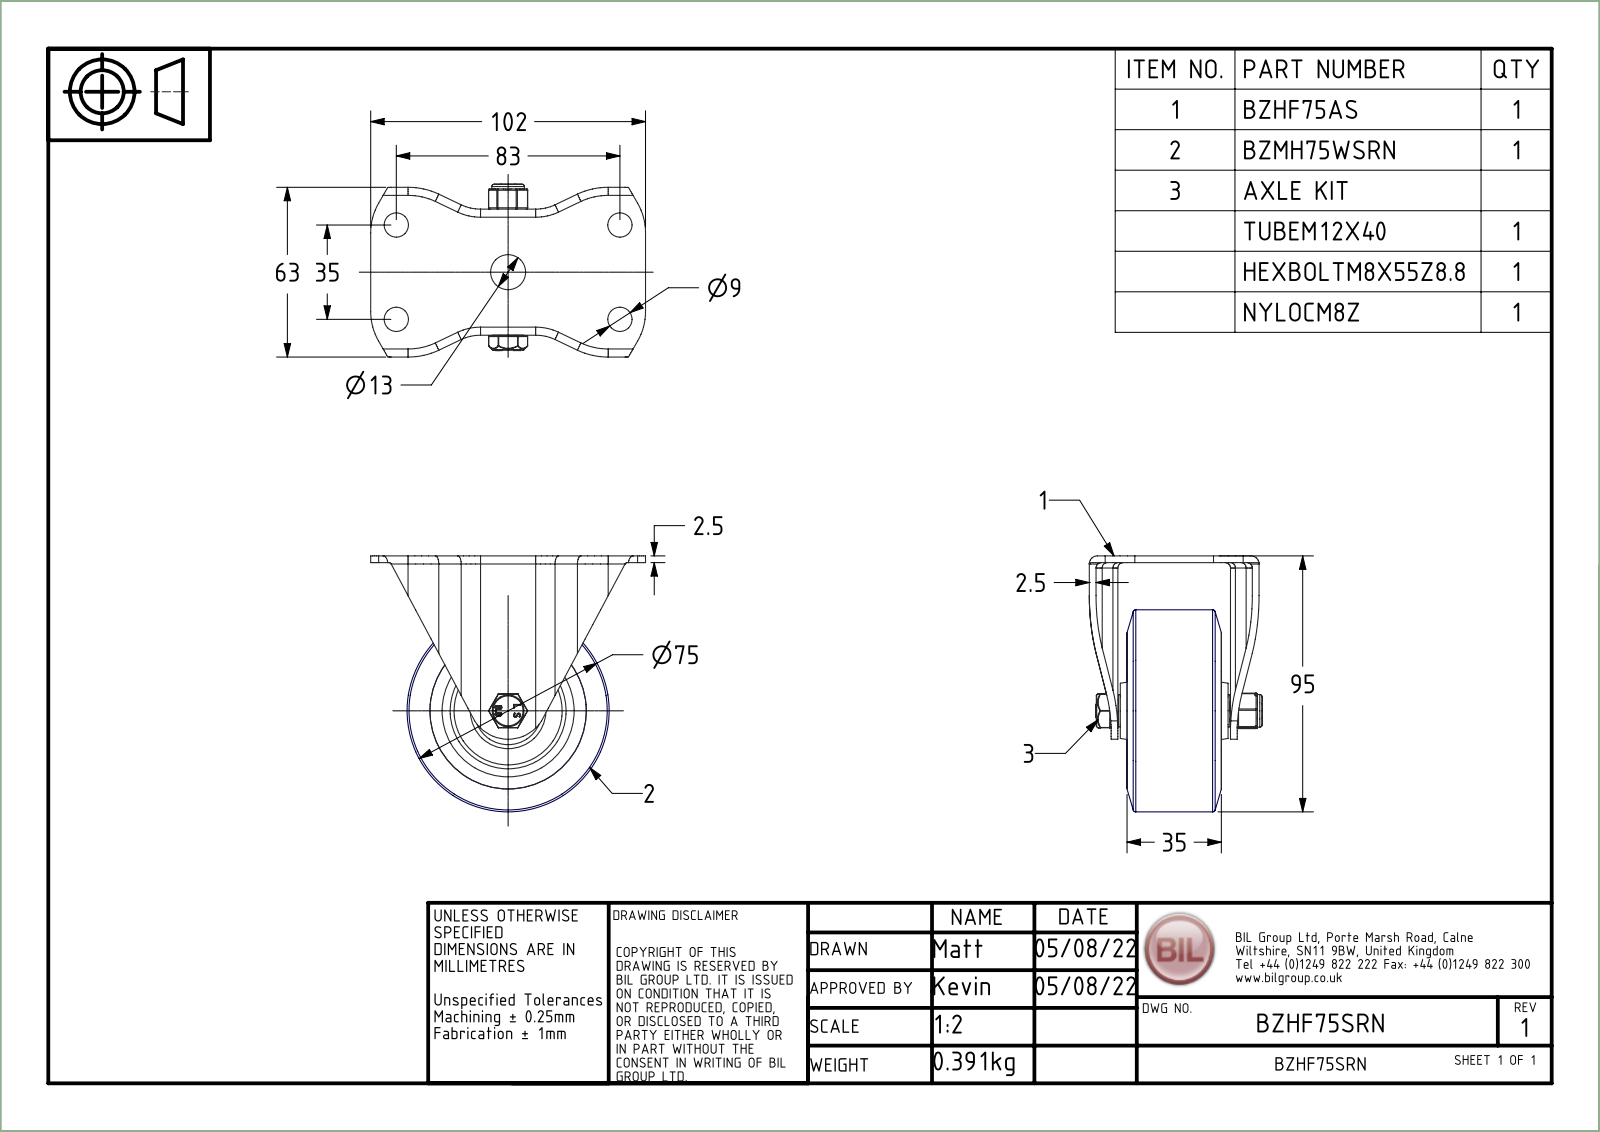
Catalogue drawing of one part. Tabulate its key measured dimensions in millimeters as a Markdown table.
| quantity | value |
| --- | --- |
| part name | BZHF75AS; ZINC PLATED, PRESSED STEEL BRACKET; BZHF75SRN; BZMH75WSRN (+8 more) |
| STEP written by | Spatial InterOp 3D (AUTOMOTIVE_DESIGN) |
| units | millimeters |
| bodies | 7 solids, 430 faces (97 planar, 213 cylindrical, 120 other) |
| overall size | 102 × 95 × 64.15 |
| volume | 149 419 mm³ |
| surface area | 66 315 mm² |
| round holes (diameter × count) | 9 × 4, 0.66 × 2, 8 × 1, 8.2 × 1, 8.4 × 1, 8.6 × 1, 12.2 × 1, 13 × 1, 58 × 1 |
| round bosses / shafts (diameter × count) | 75 × 1, 12.1 × 1, 11.9 × 1, 11.5 × 1, 6.75 × 1 |
| partial cylindrical surfaces (radius × count) | 0.5 × 18, 0.25 × 12, 2 × 8, 3 × 8, 0.33 × 4, 0.64 × 4, 17 × 4, 19.5 × 4 |
| main face-to-face distances | 2.5, 44.3, 3.4, 40.9, 5.9, 38.4, 14, 46.8, 19.9, 26.9 |
| hole center spacings | 45.04, 3.21, 35, 83, 90.08, 2.49 |
